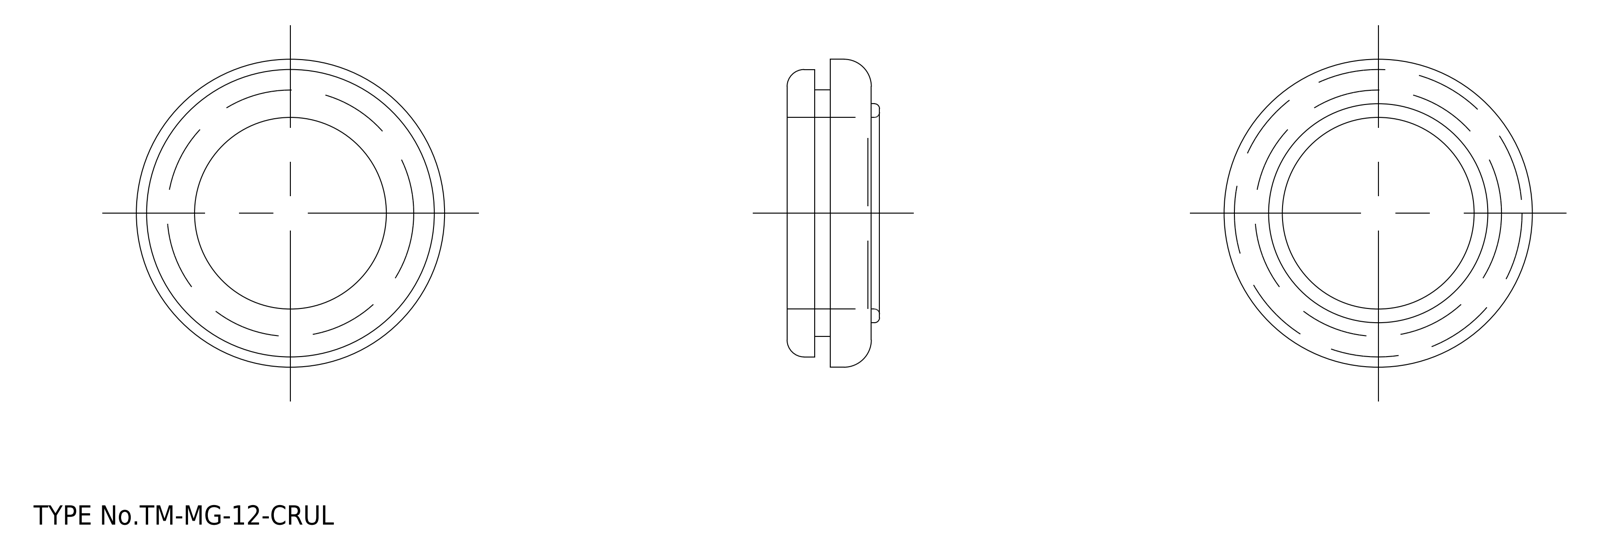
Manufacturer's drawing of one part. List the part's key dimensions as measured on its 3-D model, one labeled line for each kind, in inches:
STEP written by: spGate 15.6.1 (AUTOMOTIVE_DESIGN)
Units: inches
Bodies: 1 solid, 27 faces (7 planar, 12 cylindrical, 8 other)
Overall size (bounding box): 1.772 × 1.772 × 0.531
Volume: 0.593 in³ · Surface area: 9.861 in²
Round holes (diameter × count): ⌀1.102 ×1
Round bosses / shafts (diameter × count): ⌀1.772 ×1, ⌀1.654 ×1, ⌀1.417 ×1, ⌀1.26 ×1
Main face-to-face distances: 0.02, 0.217, 0.236, 0.248, 0.465, 0.484, 0.157, 0.091, 0.307, 0.327
